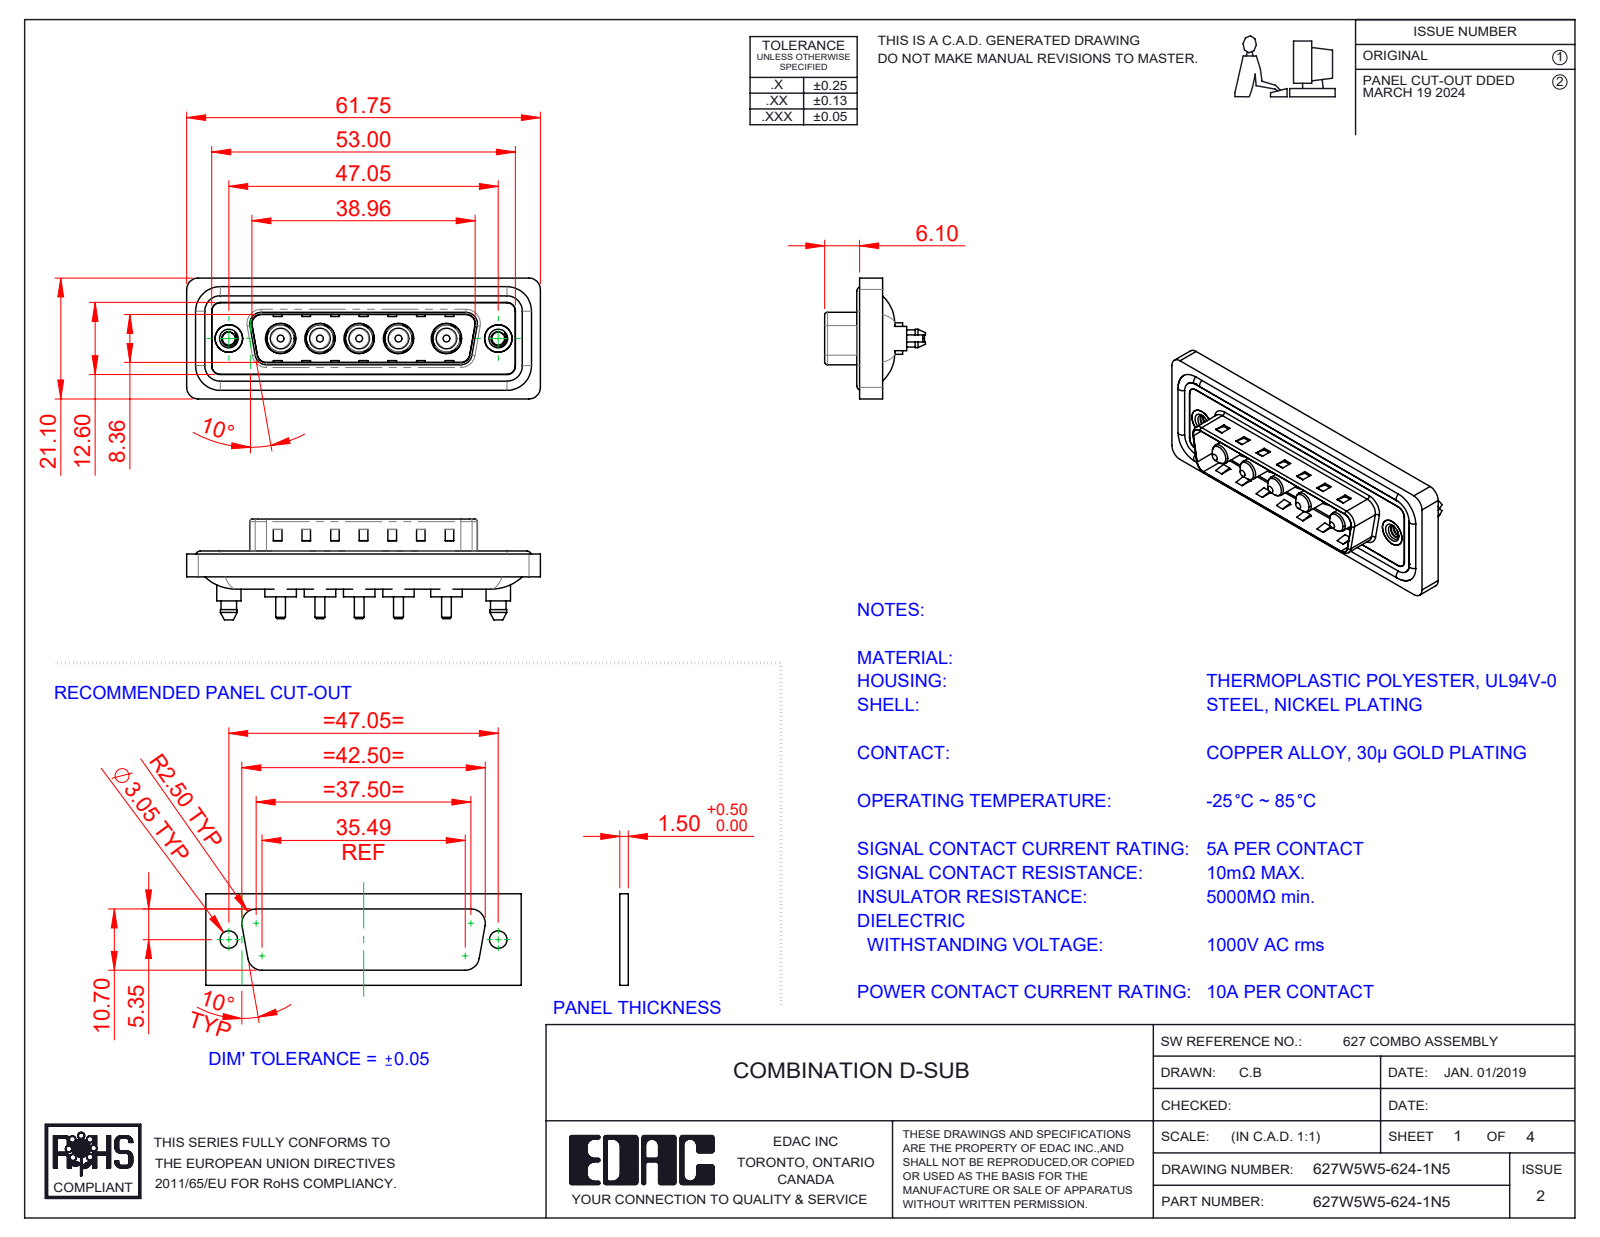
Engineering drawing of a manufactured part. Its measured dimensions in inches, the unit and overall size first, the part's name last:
Units: inches
Overall size (bounding box): 2.431 × 0.831 × 0.693
Round holes (diameter × count): ⌀0.191 ×5, ⌀0.209 ×5, ⌀0.089 ×2, ⌀0.157 ×2, ⌀0.189 ×2, ⌀0.197 ×2
Round bosses / shafts (diameter × count): ⌀0.217 ×5, ⌀0.205 ×5, ⌀0.187 ×5, ⌀0.148 ×5, ⌀0.142 ×5, ⌀0.067 ×5, ⌀0.063 ×4, ⌀0.213 ×2
Partial cylindrical surfaces — rounded edges, fillets, slot ends (radius × count): R0.059 ×24, R0.079 ×18, R0.063 ×10, R0.02 ×8, R0.083 ×5, R0.01 ×4, R0.024 ×4, R0.026 ×4
Main face-to-face distances: 0.016, 0.059, 0.043, 0.02, 0.122, 0.063, 0.114, 0.032, 0.377, 0.222
Hole centre spacings: 0.27, 0.356, 0.541, 1.496, 0.27, 0.33, 0.33, 0.356
Volume: 0.46 in³ · Surface area: 18.7 in²
Bodies: 17 solids, 728 faces (275 planar, 315 cylindrical, 138 other)
Part name (STEP PRODUCT): 627W5W5-624-1N5; 627Combo Shell Front_25 Contacts; 627Combo Threaded Boardlock_5; Power Pin_10A S (+3 more)
STEP written by: SolidWorks 2023 (CONFIG_CONTROL_DESIGN)
